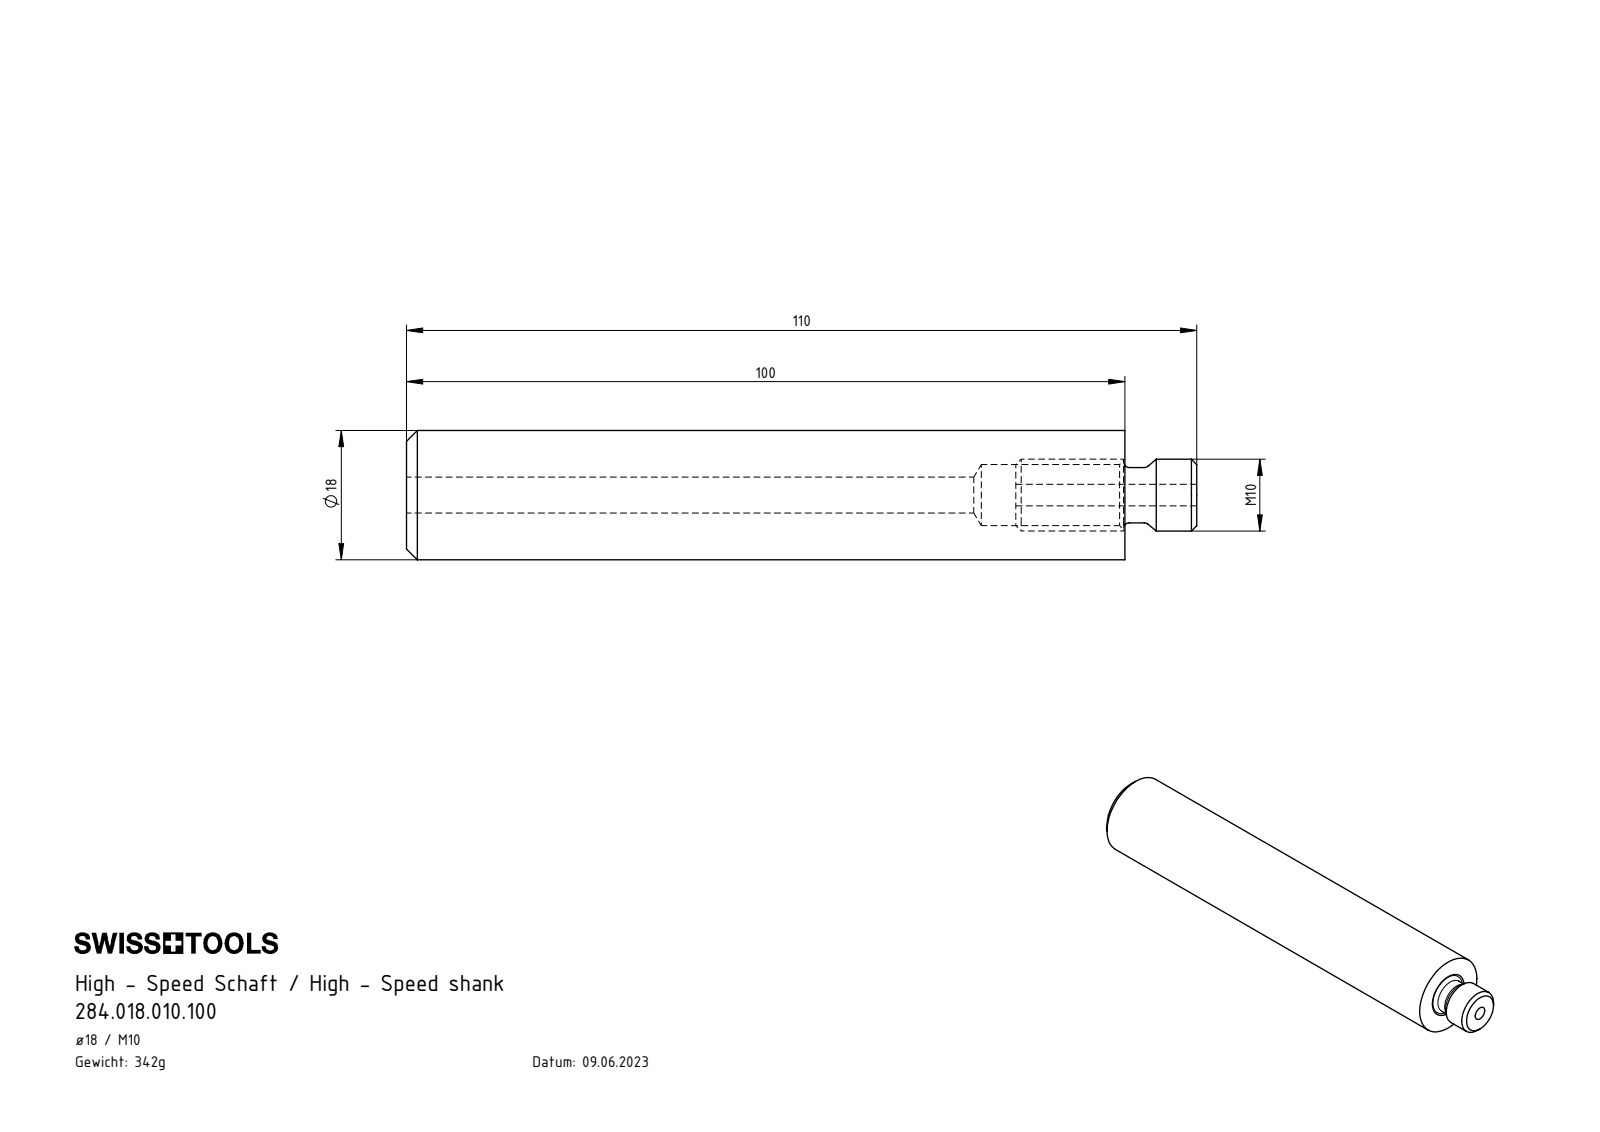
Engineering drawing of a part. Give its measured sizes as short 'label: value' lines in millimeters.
name: HM1-BG1.010.025_A; HM1-U18.001.100_A; 284.018.010.100
written by: SolidWorks 2022 (CONFIG_CONTROL_DESIGN)
unit: mm
bodies: 2 solids, 35 faces (5 planar, 14 cylindrical, 16 other)
size: 110 × 18 × 18
volume: 24 318 mm³; area: 8 991 mm²
holes: 1× ⌀3, 1× ⌀5, 1× ⌀8.5
bosses: 1× ⌀18, 1× ⌀10, 1× ⌀7.7
face distances: 100, 110, 10, 84.8, 15.2, 25.2, 99.8, 15, 10.2
